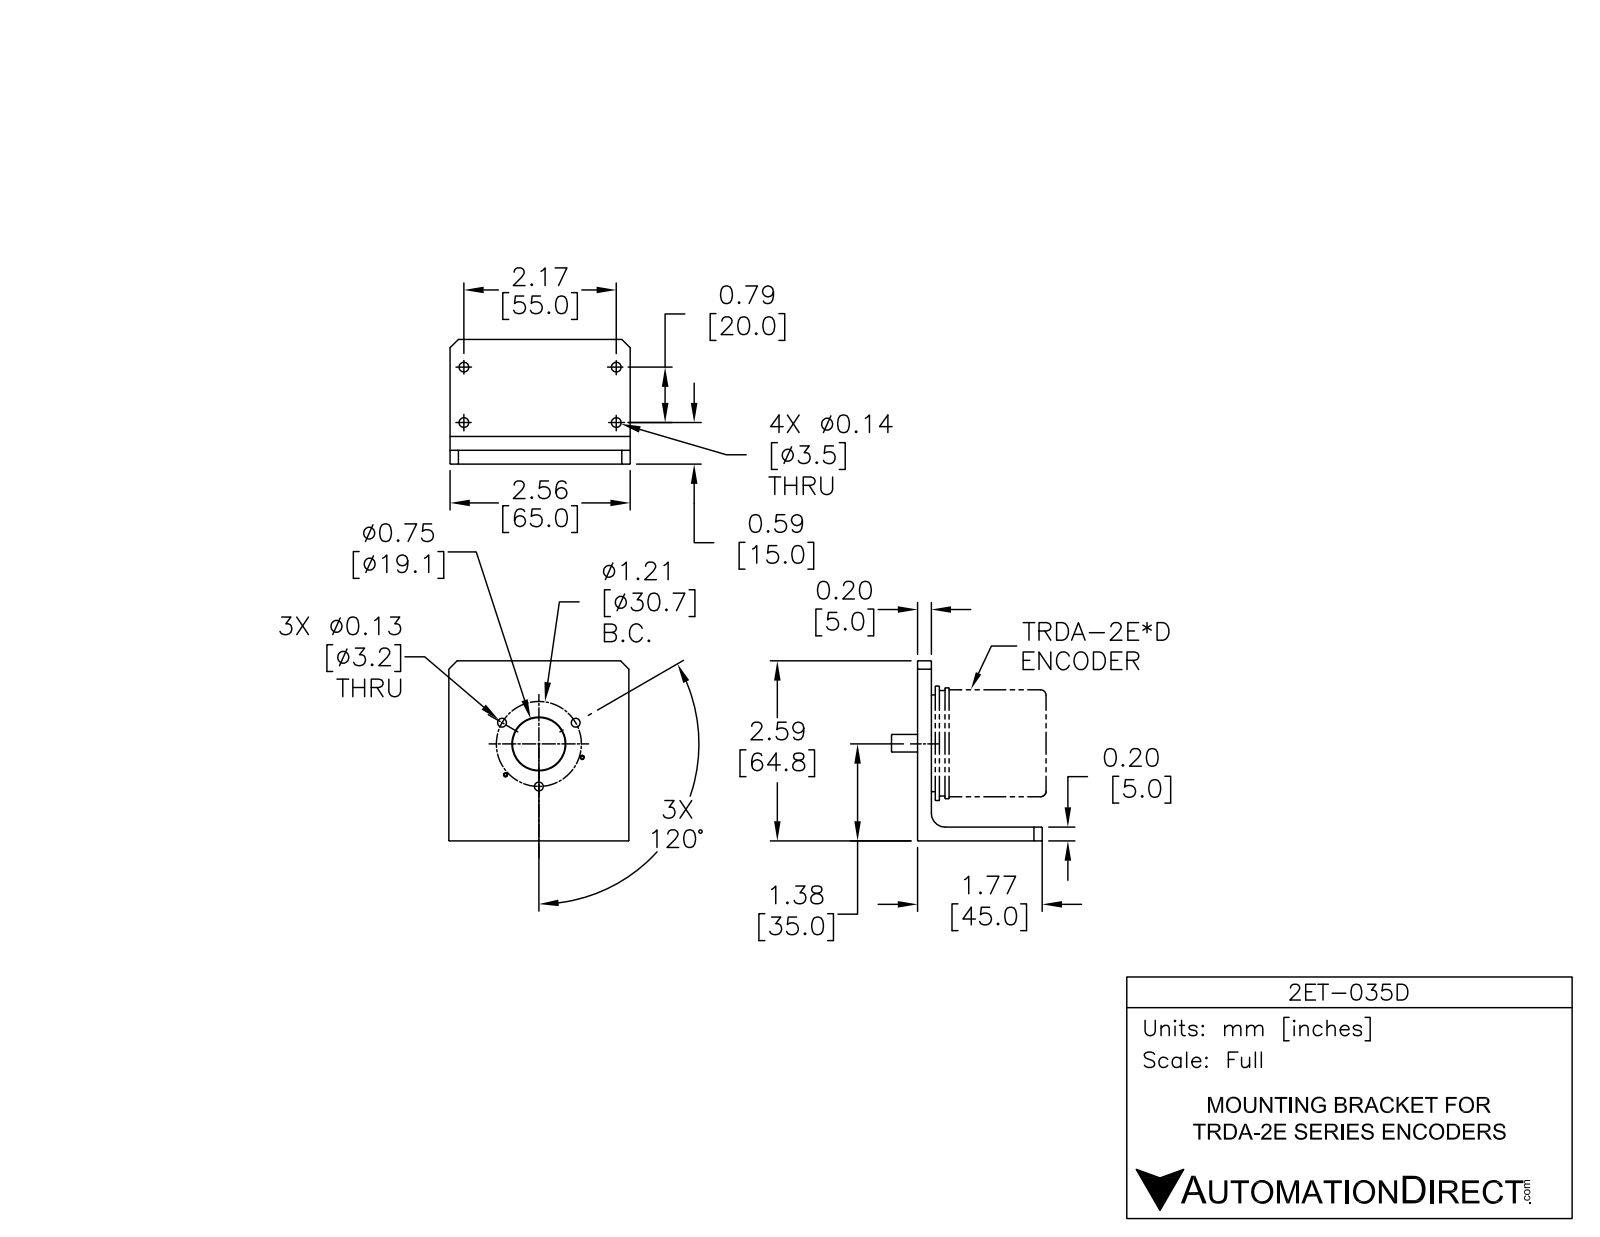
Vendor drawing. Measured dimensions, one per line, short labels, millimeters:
name: 2ET-035D
written by: SolidWorks 2016 (AUTOMOTIVE_DESIGN)
unit: mm
bodies: 1 solid, 53 faces (28 planar, 19 cylindrical, 6 other)
size: 65 × 65 × 45
volume: 32 096 mm³; area: 15 047 mm²
holes: 4× ⌀3.5, 3× ⌀3.3, 1× ⌀19.15, 1× ⌀45
rounds: 1× R5
face distances: 5, 0.4, 4.6, 65, 40, 40.4, 45, 60, 75.5, 49.21
hole spacings: 26.58, 15.34, 20, 55, 58.52, 15.35
